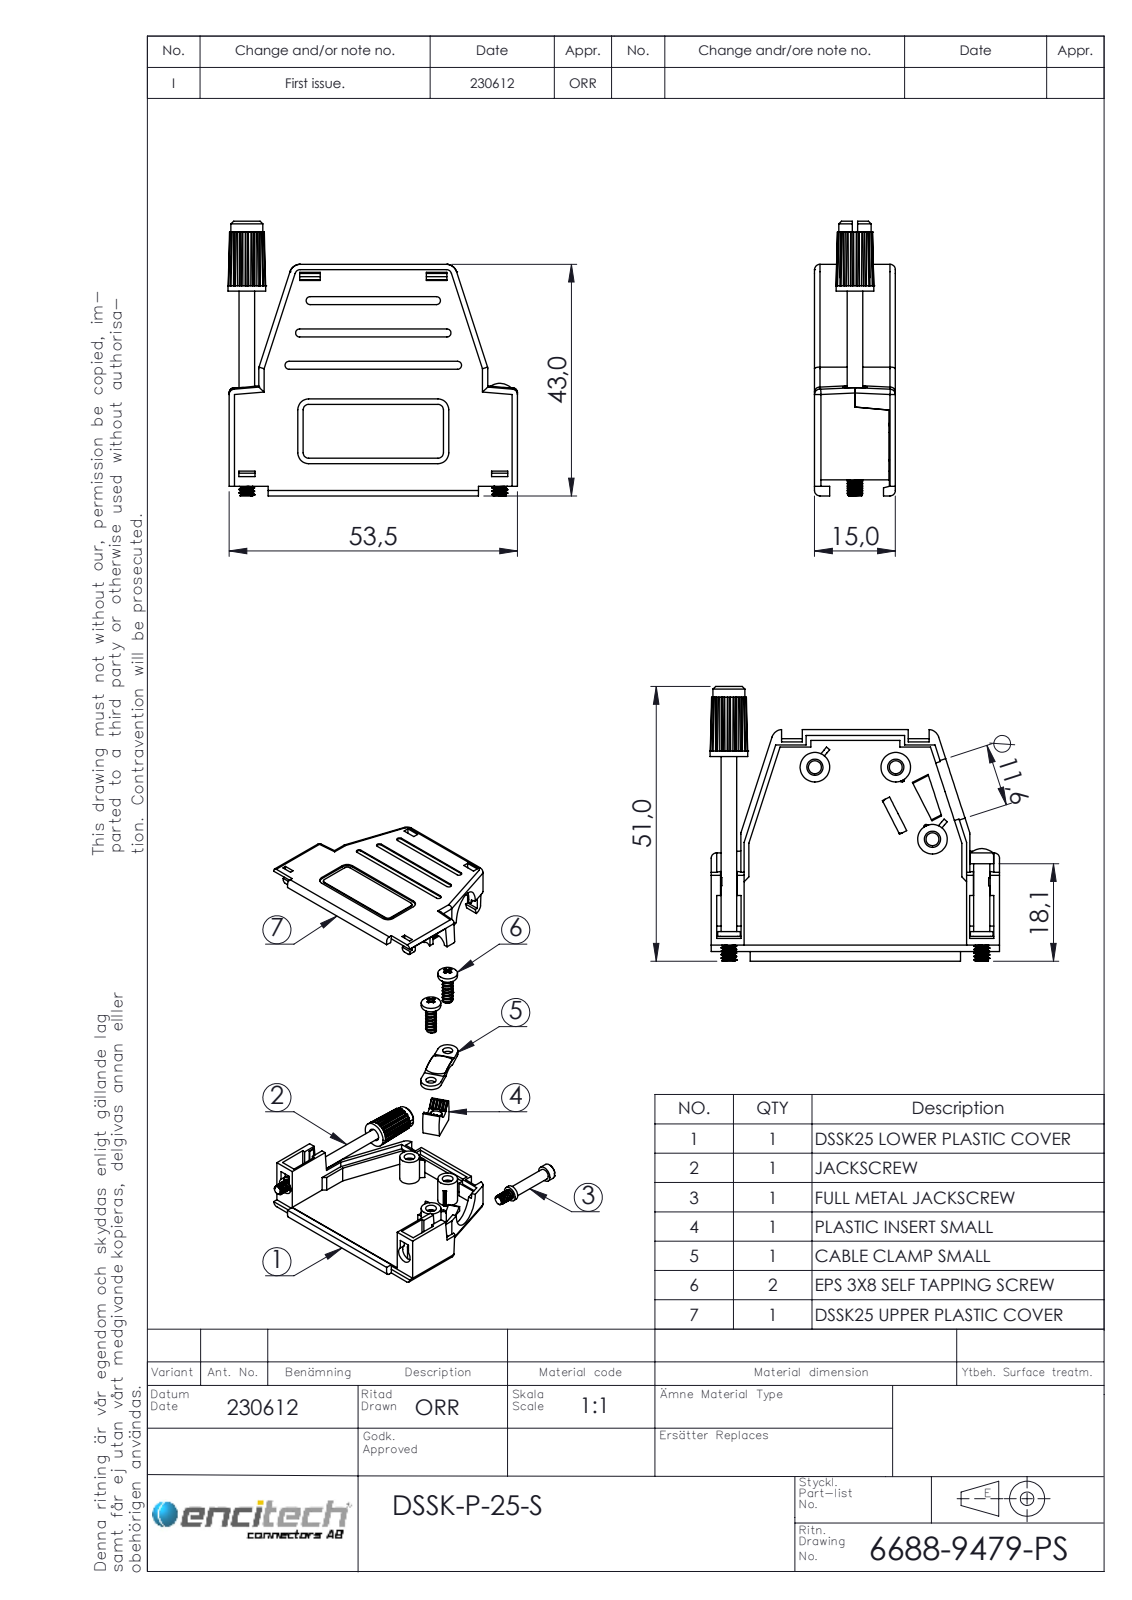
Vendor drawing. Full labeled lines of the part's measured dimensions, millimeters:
Part name (STEP PRODUCT): 6811-0132-12 Part 2; 6811-0132-12 Part 1; 6855-0109-01; Assembly of 6260-0107-13 (+4 more)
STEP written by: SolidWorks 2021 (AUTOMOTIVE_DESIGN)
Units: millimetres
Bodies: 10 solids, 845 faces (535 planar, 226 cylindrical, 84 other)
Overall size (bounding box): 53.7 × 51 × 15
Volume: 10 874 mm³ · Surface area: 15 347 mm²
Round holes (diameter × count): ⌀2.4 ×3, ⌀3 ×3, ⌀2.8 ×2, ⌀4.5 ×2, ⌀3.5 ×1, ⌀11.6 ×1
Round bosses / shafts (diameter × count): ⌀5.5 ×3, ⌀5.45 ×2, ⌀4.2 ×2, ⌀2.85 ×2, ⌀2.46 ×2, ⌀7 ×1, ⌀6 ×1, ⌀4.4 ×1
Partial cylindrical surfaces — rounded edges, fillets, slot ends (radius × count): R1 ×30, R0.75 ×13, R2 ×8, R0.1 ×4, R0.5 ×4, R0.25 ×2, R1.2 ×2, R1.5 ×2
Main face-to-face distances: 1.7, 13.3, 11.6, 15, 1.5, 2, 5.8, 14.8, 13.1, 7.3
Hole centre spacings: 7.57, 15, 18.9, 25.58, 46.9
